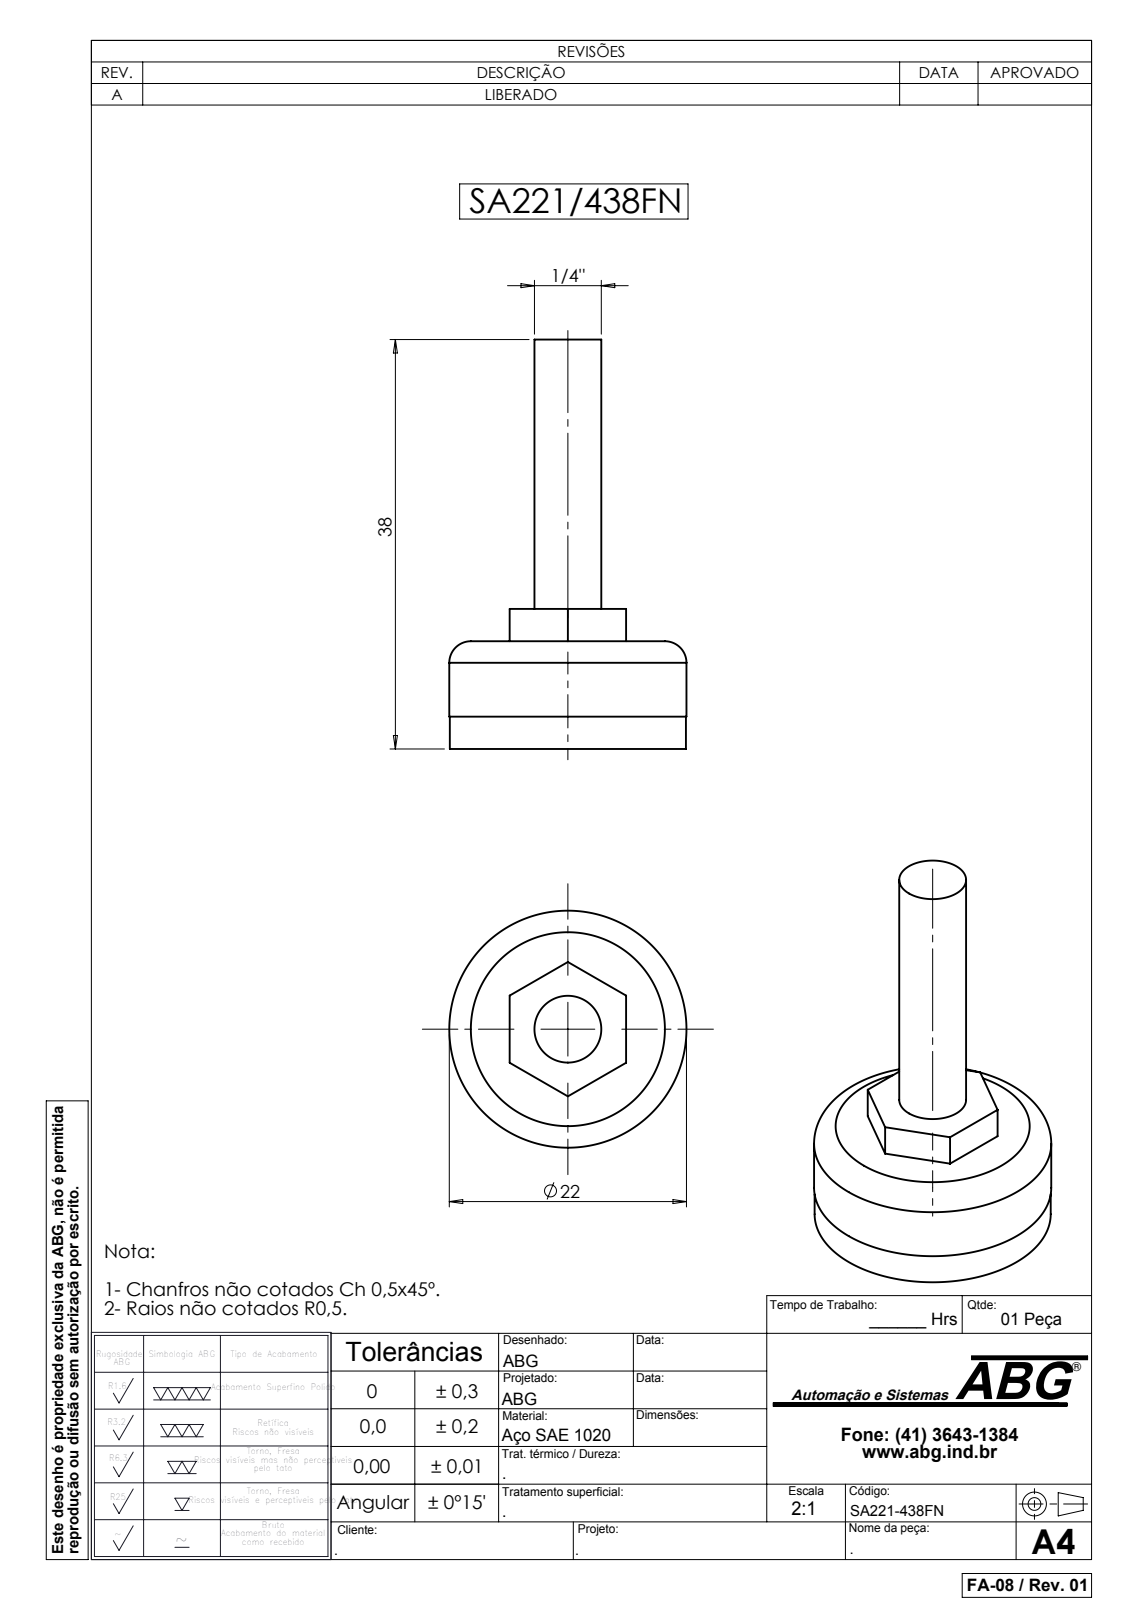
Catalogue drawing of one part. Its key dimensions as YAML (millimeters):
part_name: "SA221-438FN"
step_written_by: "SolidWorks 2007 (CONFIG_CONTROL_DESIGN)"
units: millimeters
bodies: {solids: 1, faces: 19, planar: 11, cylindrical: 6, other: 2}
overall_size: [37.5, 22, 22]
volume: 4604
surface_area: 1954
round_bosses_or_shafts:
  - {diameter: 22, count: 1}
  - {diameter: 21.9, count: 1}
  - {diameter: 6.2, count: 1}
face_to_face_distances: [9.5, 12.5, 3, 10.8, 37.5, 28, 25, 2.5, 7, 10]
